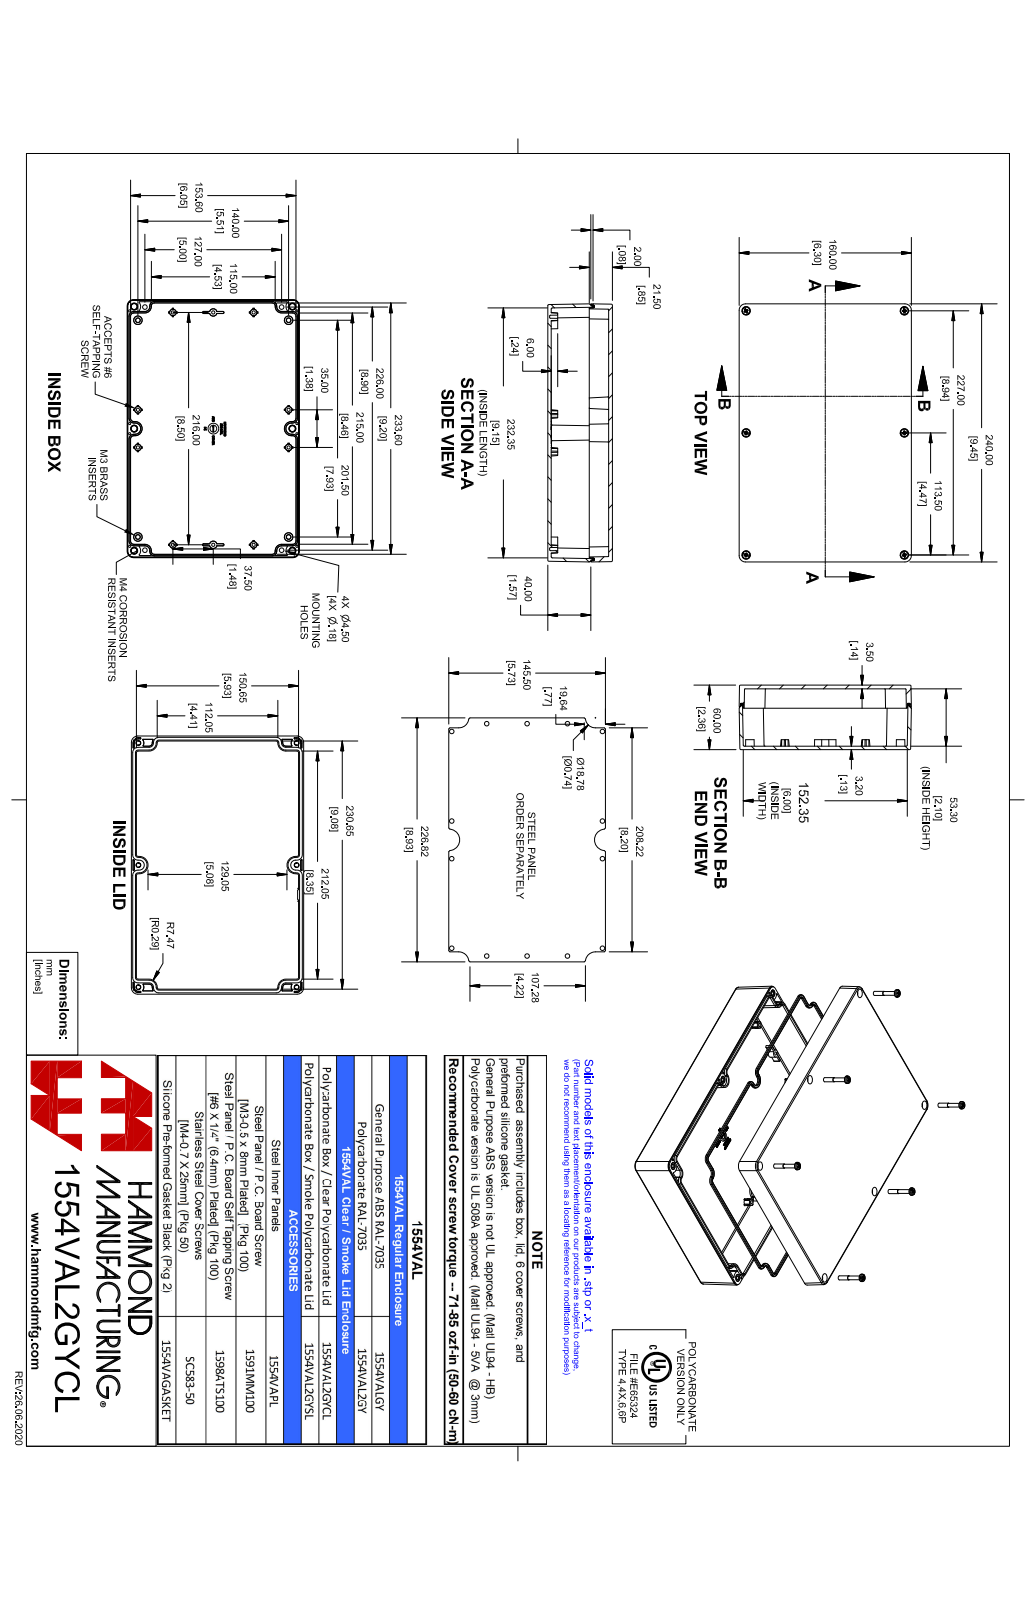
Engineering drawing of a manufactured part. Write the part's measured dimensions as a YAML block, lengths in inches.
part_name: "1554VAL2GYCL"
step_written_by: "SolidWorks 2021 (AUTOMOTIVE_DESIGN)"
units: inches
bodies: {solids: 19, faces: 2427, planar: 945, cylindrical: 438, other: 1044}
overall_size: [9.449, 6.299, 2.362]
volume: 26.52
surface_area: 432.9
round_holes:
  - {diameter: 0.128, count: 6}
  - {diameter: 0.097, count: 4}
  - {diameter: 0.181, count: 4}
  - {diameter: 0.25, count: 1}
  - {diameter: 0.394, count: 1}
round_bosses_or_shafts:
  - {diameter: 0.272, count: 6}
  - {diameter: 0.25, count: 6}
  - {diameter: 0.218, count: 6}
  - {diameter: 0.21, count: 6}
  - {diameter: 0.152, count: 6}
  - {diameter: 0.137, count: 6}
  - {diameter: 0.19, count: 4}
  - {diameter: 0.154, count: 4}
partial_cylinders:
  - {radius: 0.02, count: 33}
  - {radius: 0.012, count: 28}
  - {radius: 0.039, count: 24}
  - {radius: 0.1, count: 12}
  - {radius: 0.195, count: 12}
  - {radius: 0.236, count: 8}
  - {radius: 0.031, count: 6}
  - {radius: 0.059, count: 4}
face_to_face_distances: [0.126, 2.362, 0.138, 2.224, 2.098, 2.236, 0.185, 6.299, 6.173, 6.114]
hole_center_spacings: [0.52, 3.969, 4.469, 5.672, 6.903, 7.312, 8.436, 10.152]
